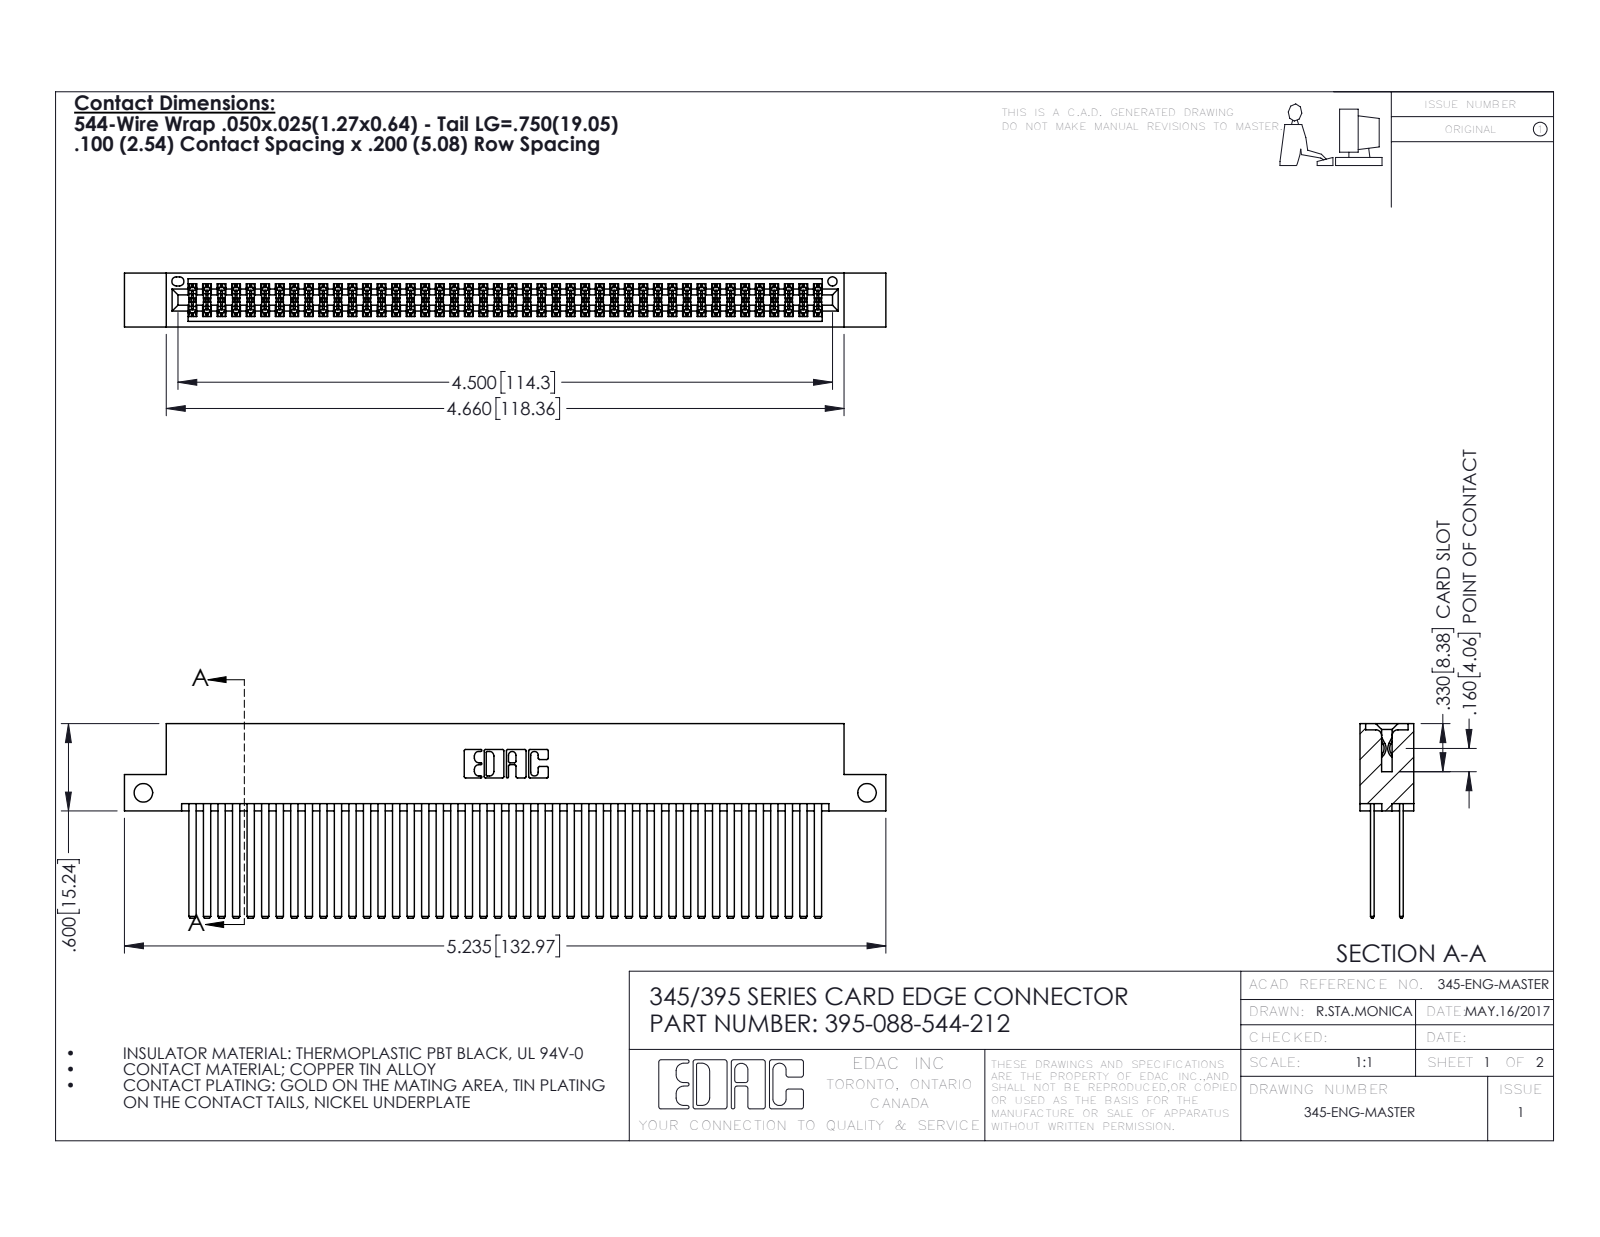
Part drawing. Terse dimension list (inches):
name: 345-292-001_345-293-144; 395-088-544-212; 345 Part_Flush Mounting Lugs - Side Mount
written by: SolidWorks 2016 (CONFIG_CONTROL_DESIGN)
unit: in
bodies: 89 solids, 3998 faces (2632 planar, 1366 cylindrical, 0 other)
size: 5.235 × 1.337 × 0.37
volume: 0.859 in³; area: 37.72 in²
holes: 2× ⌀0.128, 1× ⌀0.064
rounds: 132× R0.006, 22× R0.01, 6× R0.007, 6× R0.031, 3× R0.026, 2× R0.014, 2× R0.019, 2× R0.022
face distances: 0.2, 0.025, 0.298, 0.072, 0.098, 0.272, 0.225, 0.175, 0.37, 0.05
hole spacings: 4.975
